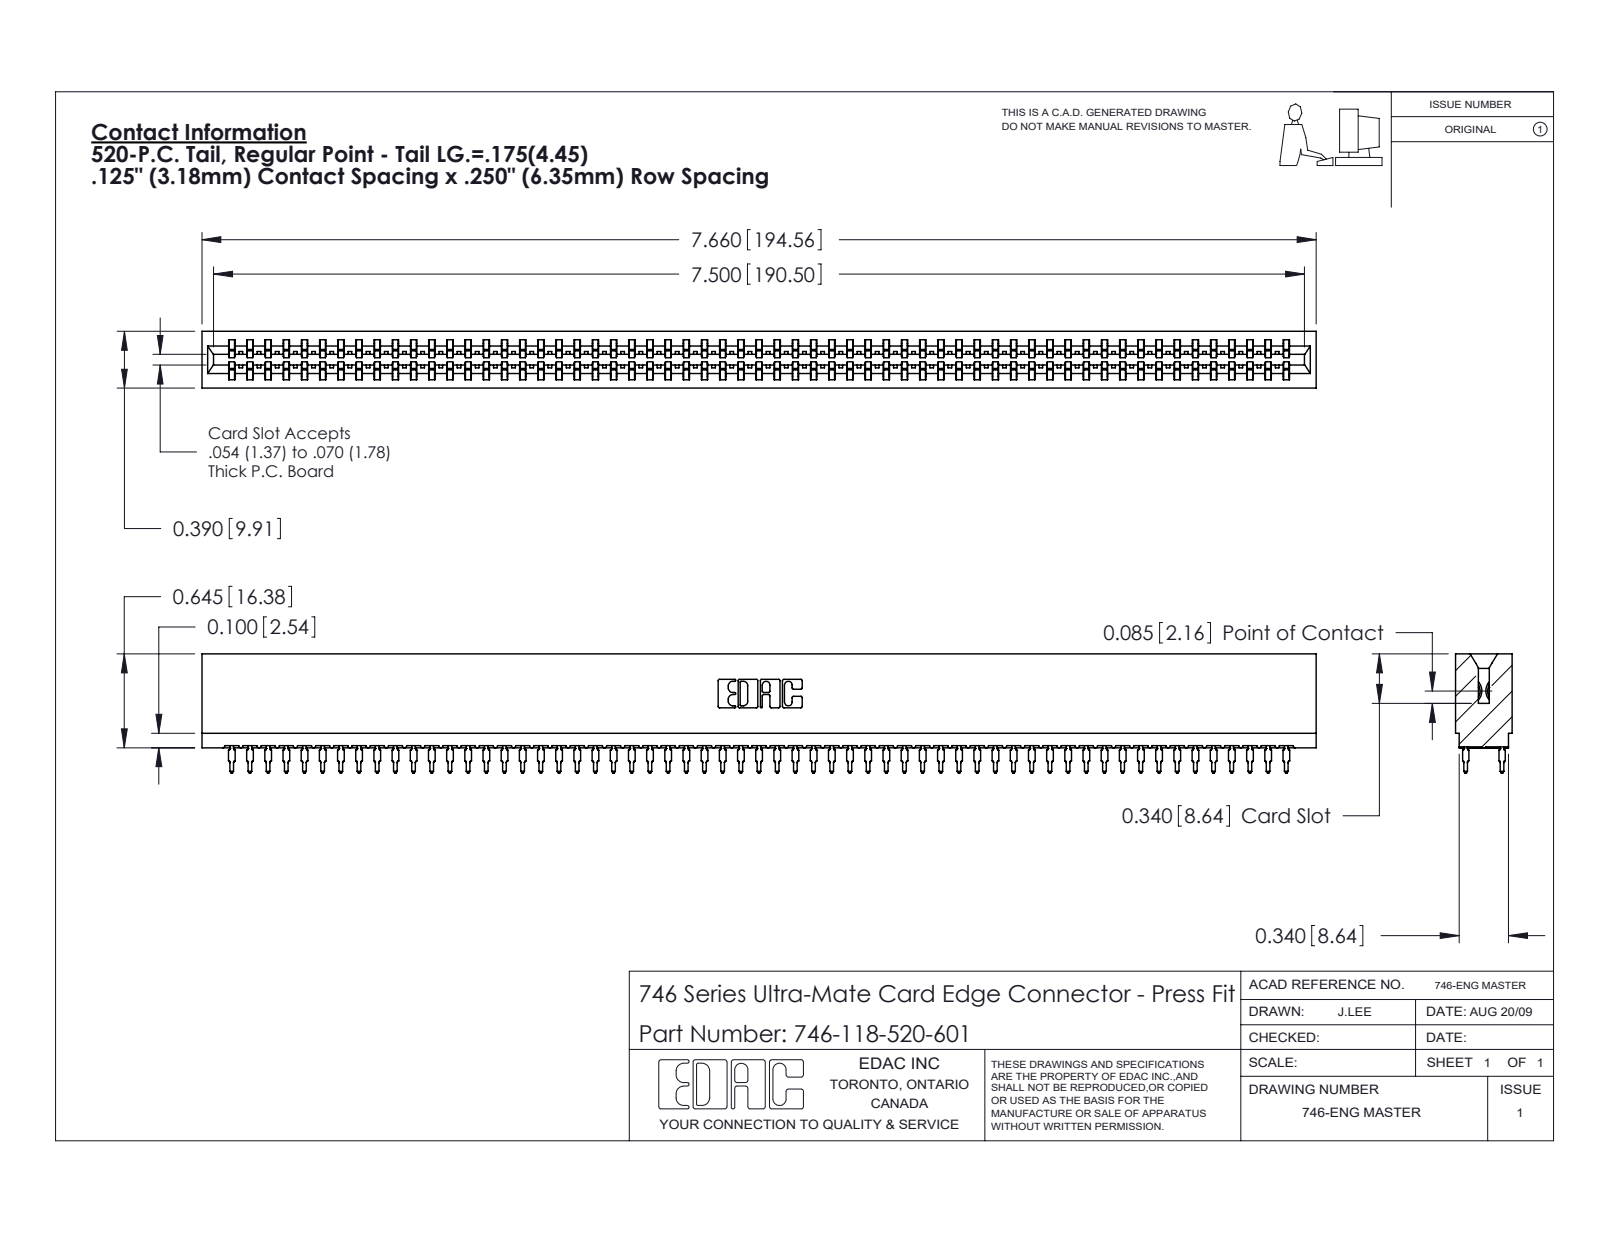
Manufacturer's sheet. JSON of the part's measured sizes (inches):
{"part_name": "746-292-001_520; 746-118-520-601; 746 Part_.340 Slot Depth - 01", "step_written_by": "SolidWorks 2020 (CONFIG_CONTROL_DESIGN)", "units": "inches", "bodies": {"solids": 119, "faces": 10658, "planar": 5483, "cylindrical": 2107, "other": 3068}, "overall_size": [7.66, 0.819, 0.39], "volume_in3": 1.354, "surface_area_in2": 50.01, "partial_cylinders_radius": [[0.021, 236], [0.015, 60], [0.01, 22], [0.005, 8], [0.011, 8], [0.007, 6], [0.031, 6], [0.026, 3]], "face_to_face_distances": [0.057, 0.333, 0.39, 0.025, 0.25, 0.307, 0.275, 0.083, 0.015, 0.059]}
